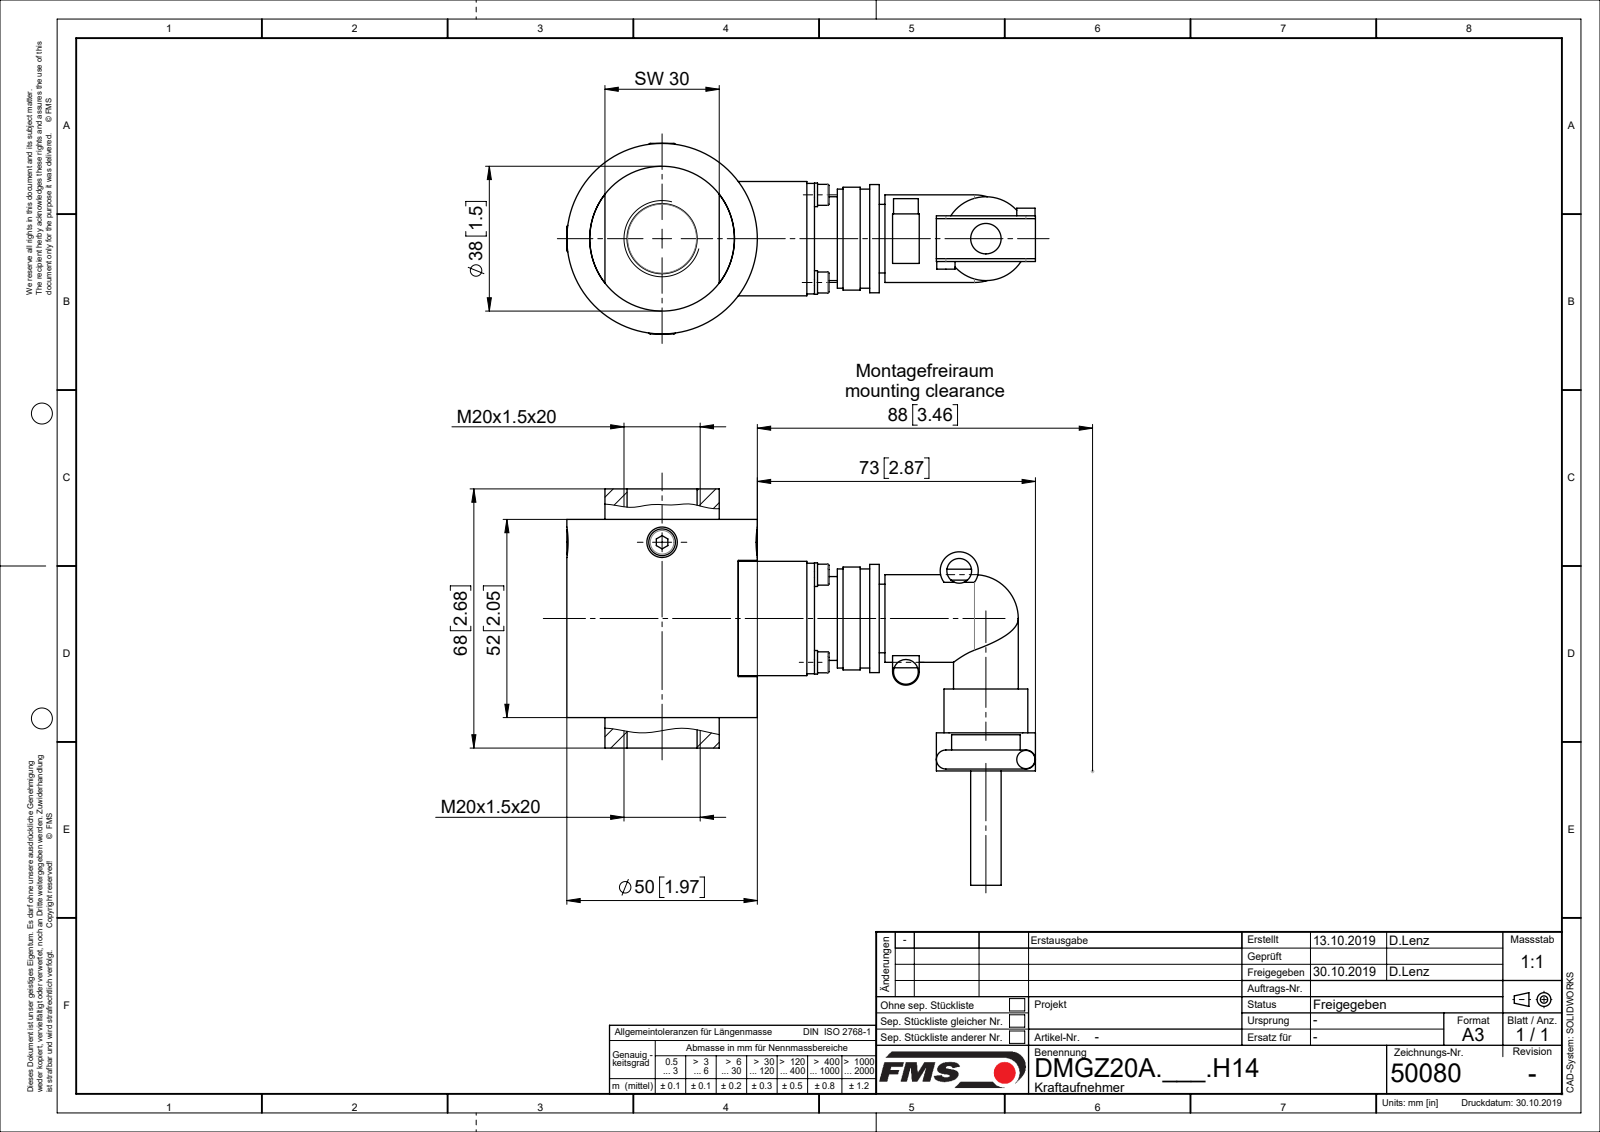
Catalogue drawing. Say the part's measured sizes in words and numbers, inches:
The part is named "D50080; L49026; TEIL1; I-6KT_SCHRAUBE_M4X10 (+6 more)". Its 3-D file was written by "Mechanical Desktop 2007 (CONFIG_CONTROL_DESIGN)". It is 16 solids with 304 faces: 105 planar, 154 cylindrical and 45 other. Overall it measures 4.843 by 4.094 by 1.969 inches. Its volume is 8.988 cubic inches and its surface area 73.6 square inches. Round holes: 6 of diameter 0.135, 4 of diameter 0.126, 4 of diameter 0.134, 4 of diameter 0.138, 2 of diameter 0.169, 2 of diameter 0.315, 1 of diameter 0.735, 1 of diameter 0.807, 1 of diameter 0.906, 1 of diameter 1.496. Round bosses or shafts: 4 of diameter 0.244, 4 of diameter 0.217, 4 of diameter 0.118, 2 of diameter 0.866, 2 of diameter 0.276, 2 of diameter 0.256, 2 of diameter 0.189, 2 of diameter 0.157. Partial cylindrical surfaces (rounded edges, fillets, slot ends): 2 of radius 0.098, 1 of radius 0.138, 1 of radius 0.197. The main face-to-face distances are 0.315, 1.181, 0.748, 2.362, 0.709, 0.433, 1.614, 1.929, 1.654, 2.047. The hole center spacings are 0.64, 0.906, 0.563, 1.281, 1.32, 0.787.
